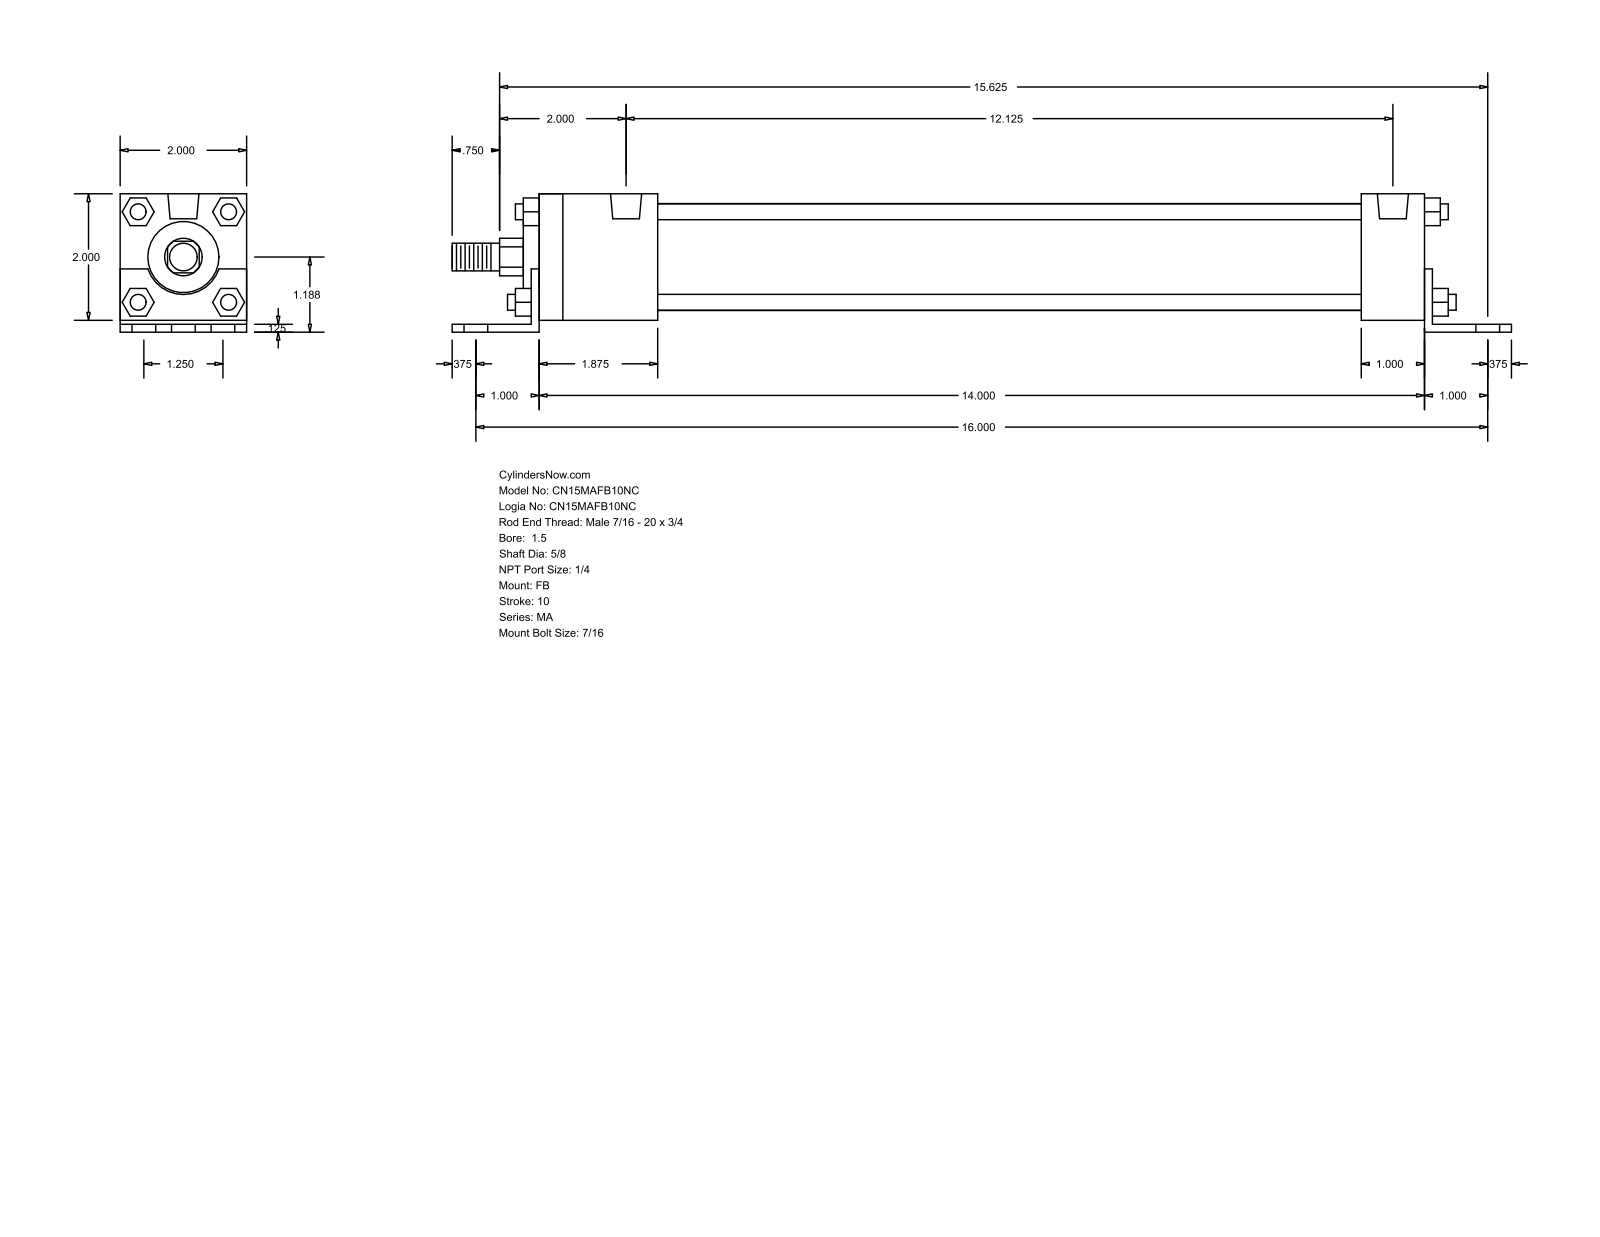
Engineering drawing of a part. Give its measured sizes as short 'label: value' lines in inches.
name: MA_FB__0150_0.625
written by: GSSL Pune (CONFIG_CONTROL_DESIGN)
unit: in
bodies: 0 solids, 140 faces (105 planar, 35 cylindrical, 0 other)
size: 16.75 × 2.187 × 2
holes: 6× ⌀0.437, 4× ⌀0.313, 2× ⌀0.492
bosses: 4× ⌀0.25, 1× ⌀1.69, 1× ⌀1.125, 1× ⌀0.625, 1× ⌀0.437
rounds: 1× R0.297, 1× R0.593
face distances: 2, 0.125, 0.187, 2.187, 0.063, 2.063, 1.125, 14.25, 0.125, 14.375
hole spacings: 0.625, 16.013, 16, 1.25, 1.626, 2.456, 12.125, 13.639
